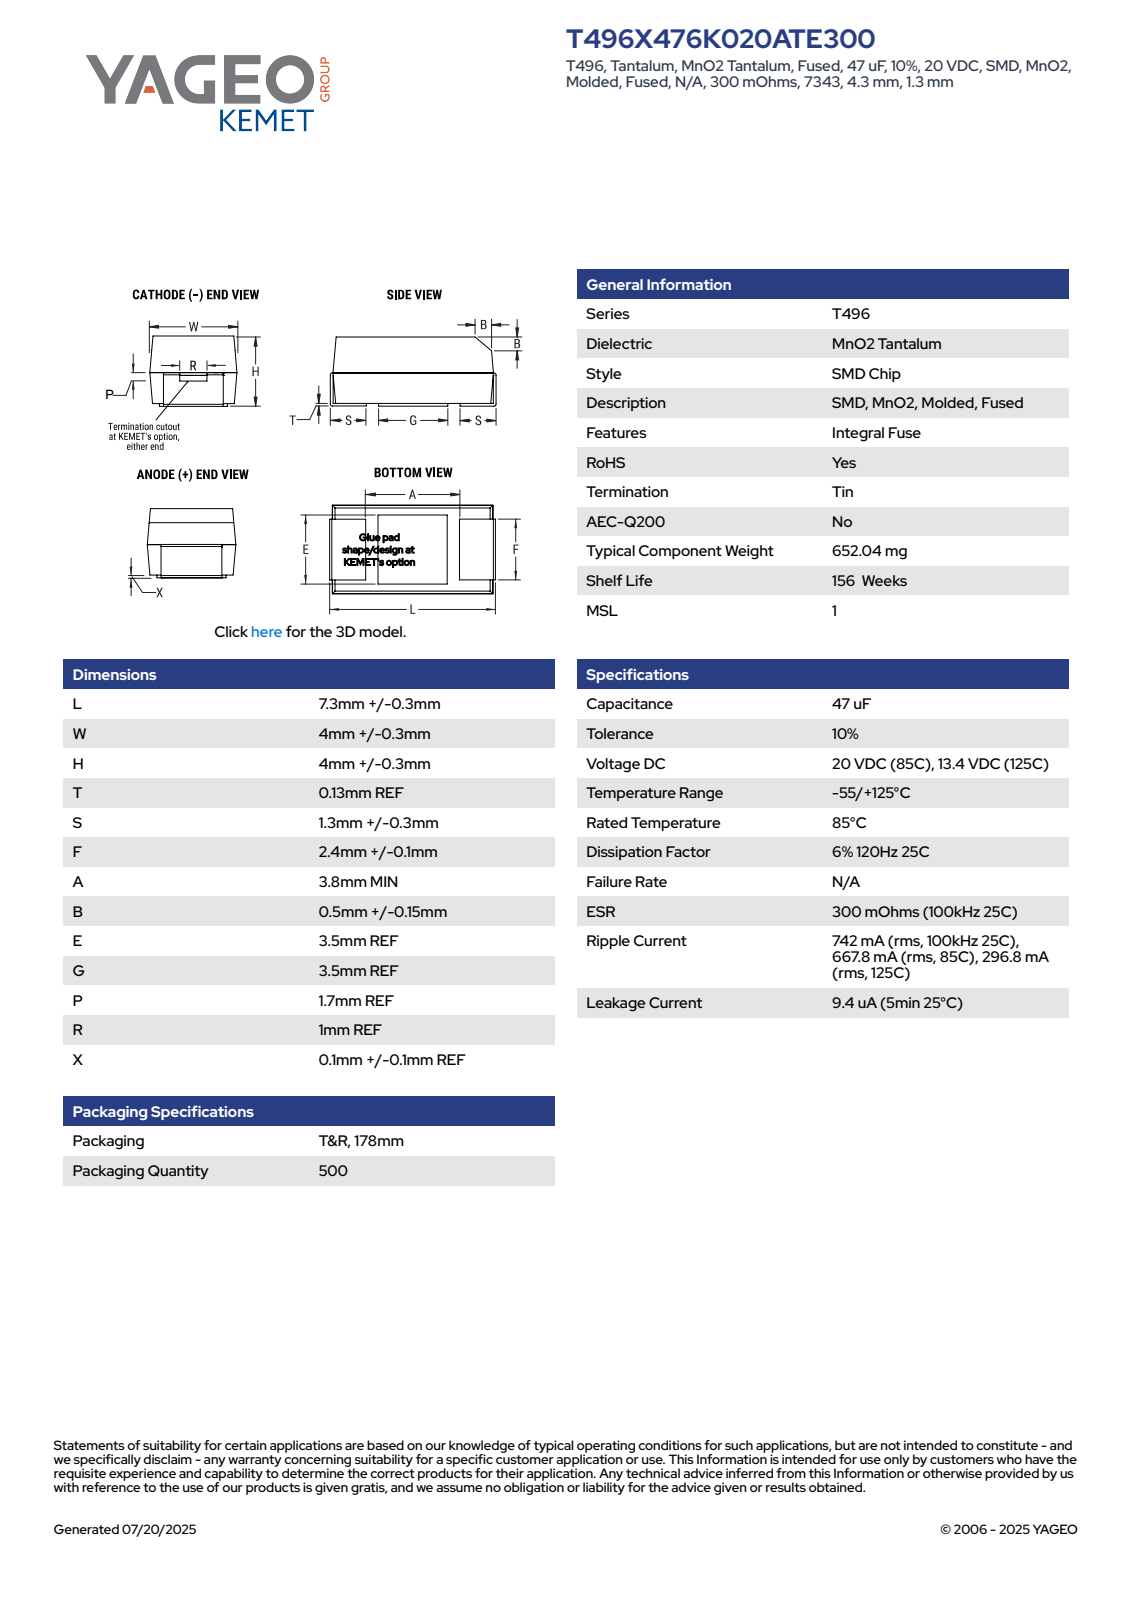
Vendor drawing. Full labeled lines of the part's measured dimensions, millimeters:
Part name (STEP PRODUCT): CTSM_TCM2NK_7343_L7.6W4.3H4.3T0.13S1.3F2.5A3.8B0.65E3.5G3.5P1.7R1X0.2
STEP written by: SolidWorks 2020 (AUTOMOTIVE_DESIGN)
Units: millimetres
Bodies: 4 solids, 100 faces (95 planar, 5 cylindrical, 0 other)
Overall size (bounding box): 7.6 × 4.3 × 4.3
Volume: 122 mm³ · Surface area: 180 mm²
Partial cylindrical surfaces — rounded edges, fillets, slot ends (radius × count): R0.1 ×4
Main face-to-face distances: 4.3, 4.28, 4.27, 4.1, 7.47, 4.17, 7.6, 7.34, 2.05, 5.55
